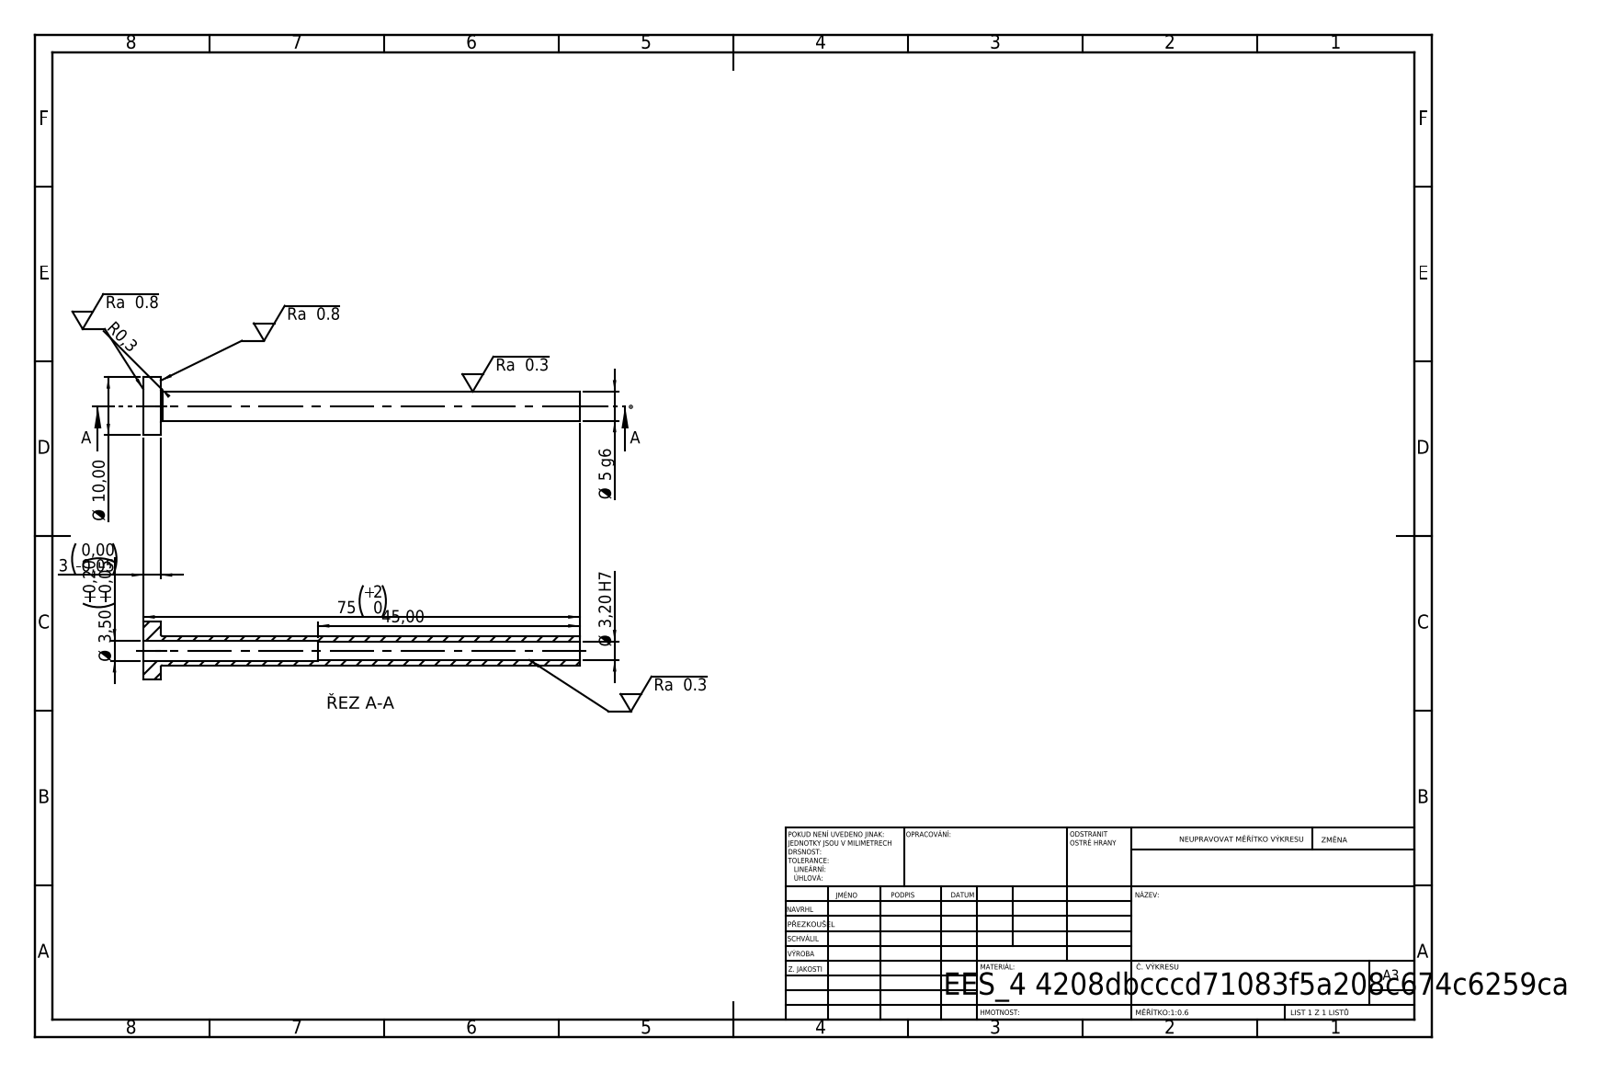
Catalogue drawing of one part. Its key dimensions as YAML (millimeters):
step_written_by: "SolidWorks 2019 (CONFIG_CONTROL_DESIGN)"
units: millimeters
bodies: {solids: 1, faces: 14, planar: 4, cylindrical: 8, other: 2}
overall_size: [75, 10, 10]
volume: 999
surface_area: 2146
round_holes:
  - {diameter: 3.2, count: 1}
  - {diameter: 3.5, count: 1}
round_bosses_or_shafts:
  - {diameter: 10, count: 1}
  - {diameter: 5, count: 1}
face_to_face_distances: [3, 75, 72, 30, 27, 45]
